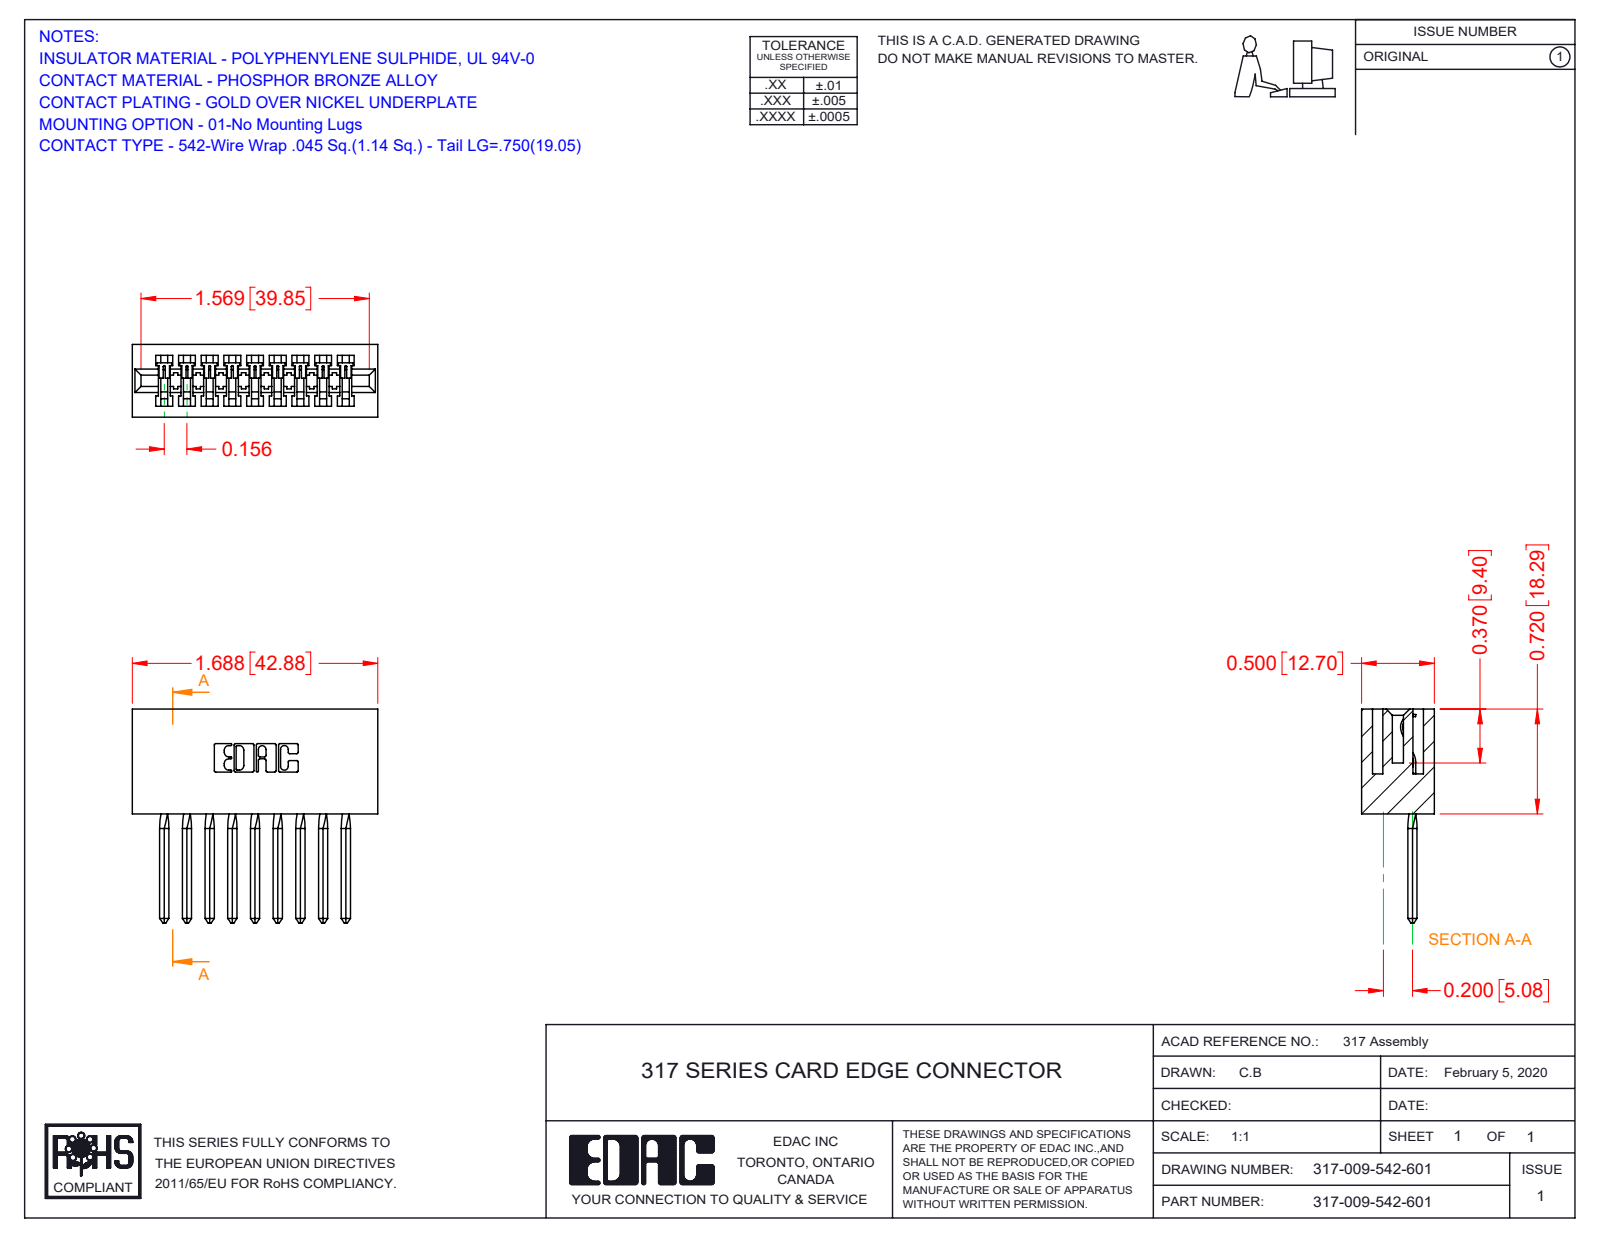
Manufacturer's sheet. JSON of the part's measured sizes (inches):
{"part_name": "317-290-003_542; 317-009-542-601; 317 Part_Lugless", "step_written_by": "SolidWorks 2016 (CONFIG_CONTROL_DESIGN)", "units": "inches", "bodies": {"solids": 10, "faces": 765, "planar": 626, "cylindrical": 103, "other": 36}, "overall_size": [1.688, 1.47, 0.5], "volume_in3": 0.447, "surface_area_in2": 12.78, "partial_cylinders_radius": [[0.01, 22], [0.006, 18], [0.007, 6], [0.031, 6], [0.026, 3], [0.074, 1], [0.089, 1], [0.1, 1]], "face_to_face_distances": [0.5, 0.075, 0.425, 0.11, 0.156, 0.065, 0.22, 0.624, 0.116, 0.312]}
